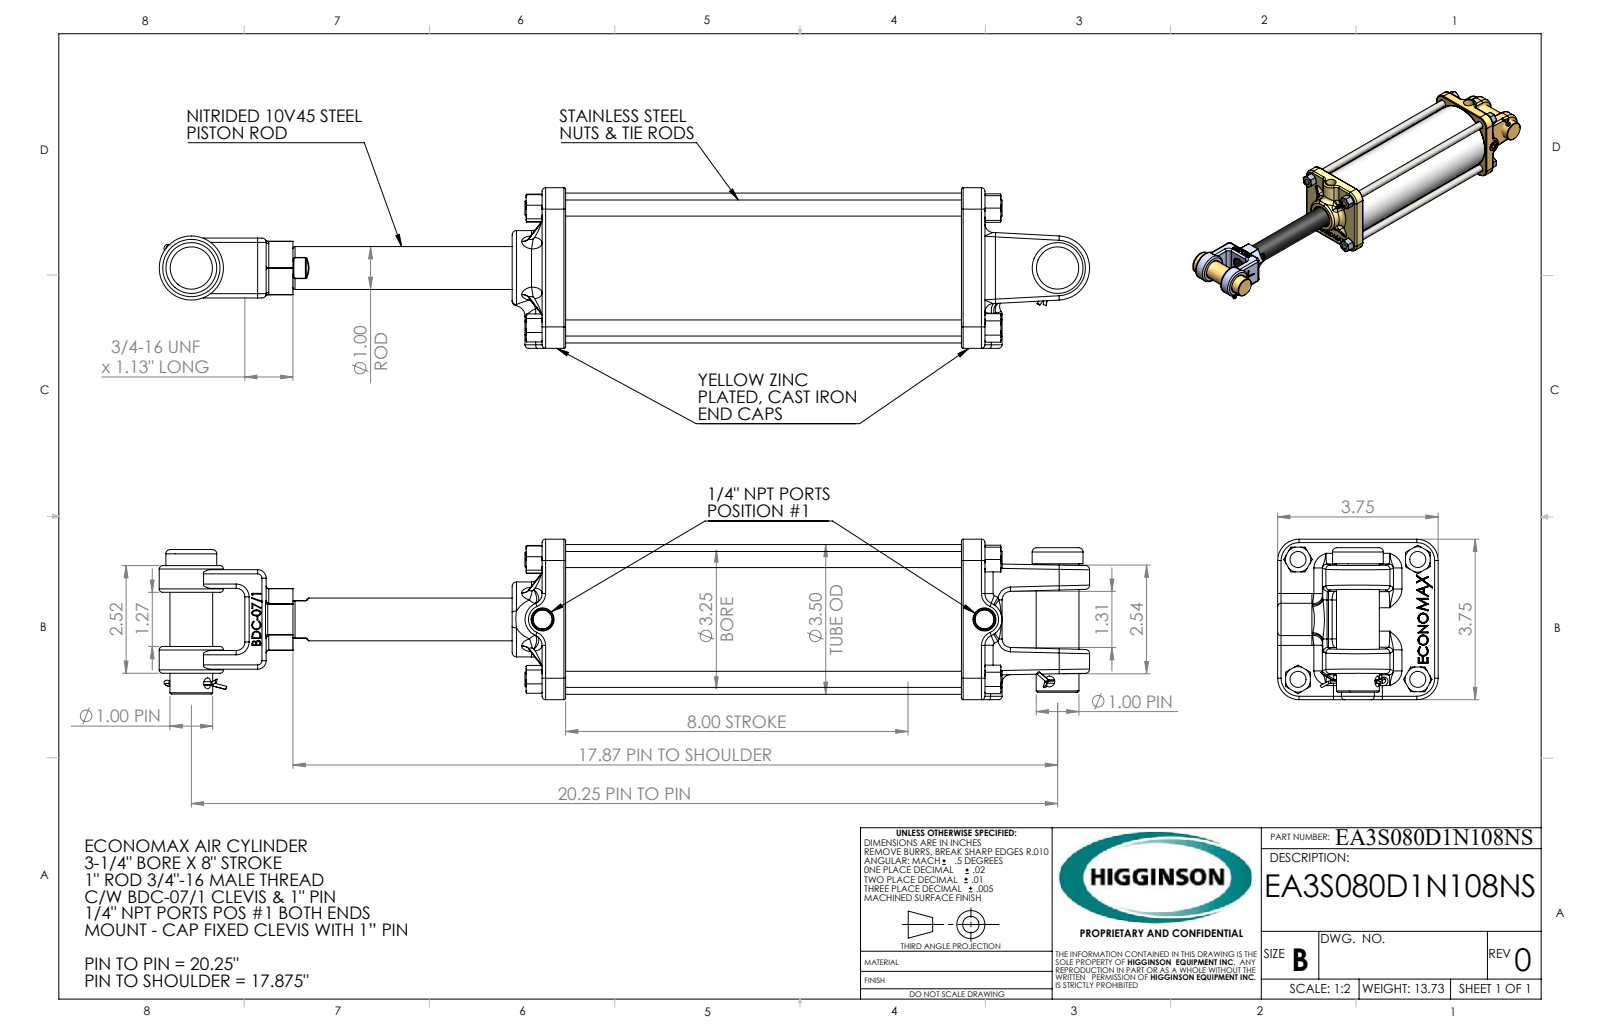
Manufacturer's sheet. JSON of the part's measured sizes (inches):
{"part_name": "CLPY-1000-3000; 18cotter pin X 1; 5409-04V; BDC-07-1 (+8 more)", "step_written_by": "SolidWorks 2021 (CONFIG_CONTROL_DESIGN)", "units": "inches", "bodies": {"solids": 23, "faces": 1449, "planar": 376, "cylindrical": 218, "other": 855}, "overall_size": [21.747, 3.75, 3.75], "volume_in3": 67.25, "surface_area_in2": 527, "round_holes": [[0.254, 2], [0.688, 1], [0.75, 1], [0.754, 1], [0.785, 1], [1.002, 1], [1.05, 1], [1.128, 1], [1.14, 1], [1.142, 1], [1.371, 1], [1.379, 1]], "round_bosses_or_shafts": [[0.375, 4], [1, 3], [1.188, 2], [3.5, 1], [3.242, 1], [3.235, 1], [2.99, 1], [2.878, 1]], "partial_cylinders_radius": [[0.1, 20], [0.2, 17], [0.039, 8], [0.04, 8], [0.08, 8], [0.25, 7], [0.01, 6], [0.02, 6]], "face_to_face_distances": [0.55, 9.8, 9.25, 1.25, 8, 8.55, 1.8, 10.35, 1.24, 0.425], "hole_center_spacings": [20.25]}
